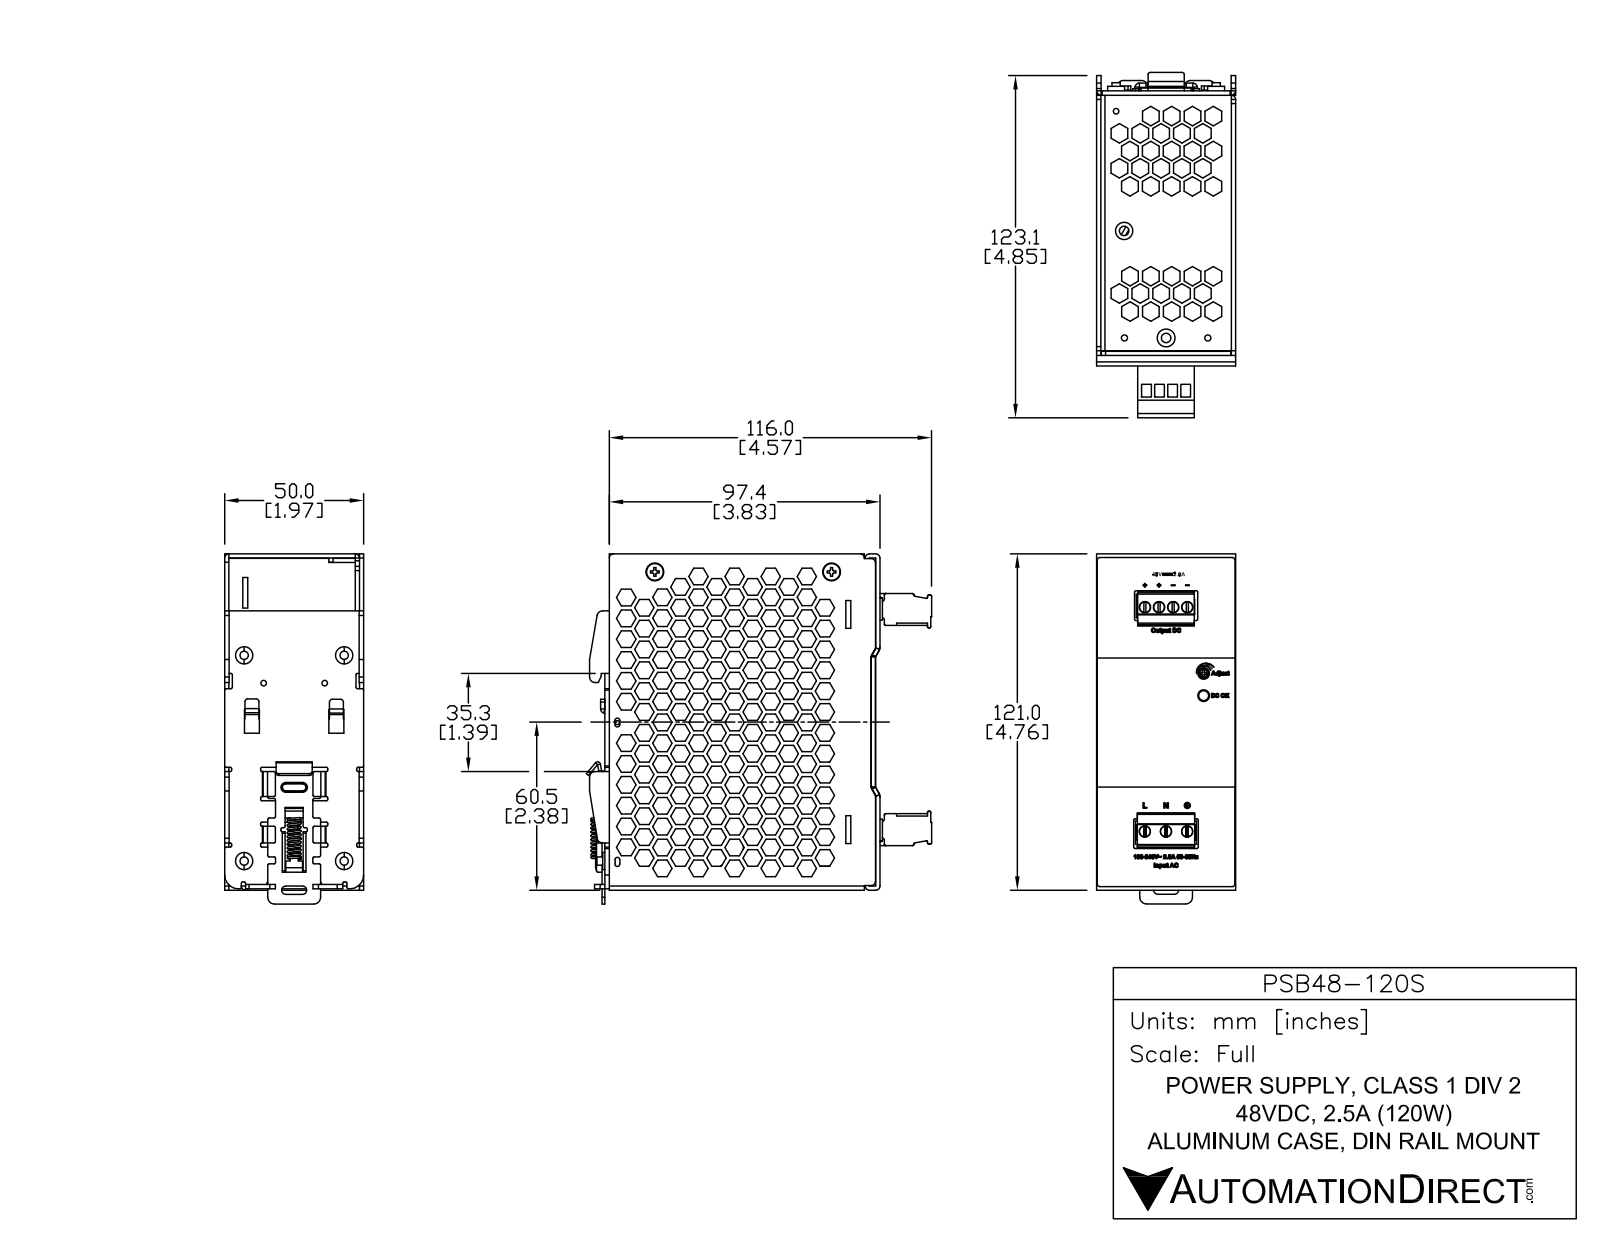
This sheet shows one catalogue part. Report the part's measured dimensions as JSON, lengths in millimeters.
{"part_name": "EE_LED1; ASSY_LATCH_50X100_ASM_2; 3050252046_1; 330301760000_1 (+8 more)", "step_written_by": "SolidWorks 2014 (AUTOMOTIVE_DESIGN)", "units": "millimeters", "bodies": {"solids": 31, "faces": 4605, "planar": 3359, "cylindrical": 688, "other": 558}, "overall_size": [126.1, 125, 50.1], "volume_mm3": 97860, "surface_area_mm2": 148900, "round_holes": [[2.5, 8], [4, 7], [3, 5], [3.5, 4], [0.5, 3], [2, 3], [0.2, 2], [1.3, 2], [2.2, 2], [3.6, 2], [4, 2], [2.8, 1]], "round_bosses_or_shafts": [[4, 7], [2.5, 7], [6, 6], [5.5, 6], [3, 6], [5.2, 4], [4, 4], [2.7, 4]], "partial_cylinders_radius": [[0.5, 128], [1.5, 32], [1, 24], [0.1, 20], [0.4, 20], [0.2, 14], [0.8, 14], [2, 14]], "face_to_face_distances": [1.5, 1.6, 48.5, 6.5, 8.1, 6.6, 5, 87, 96.5, 47], "hole_center_spacings": [5.1, 15, 30, 52.9, 70.3, 2.5, 7.6, 7.8]}
